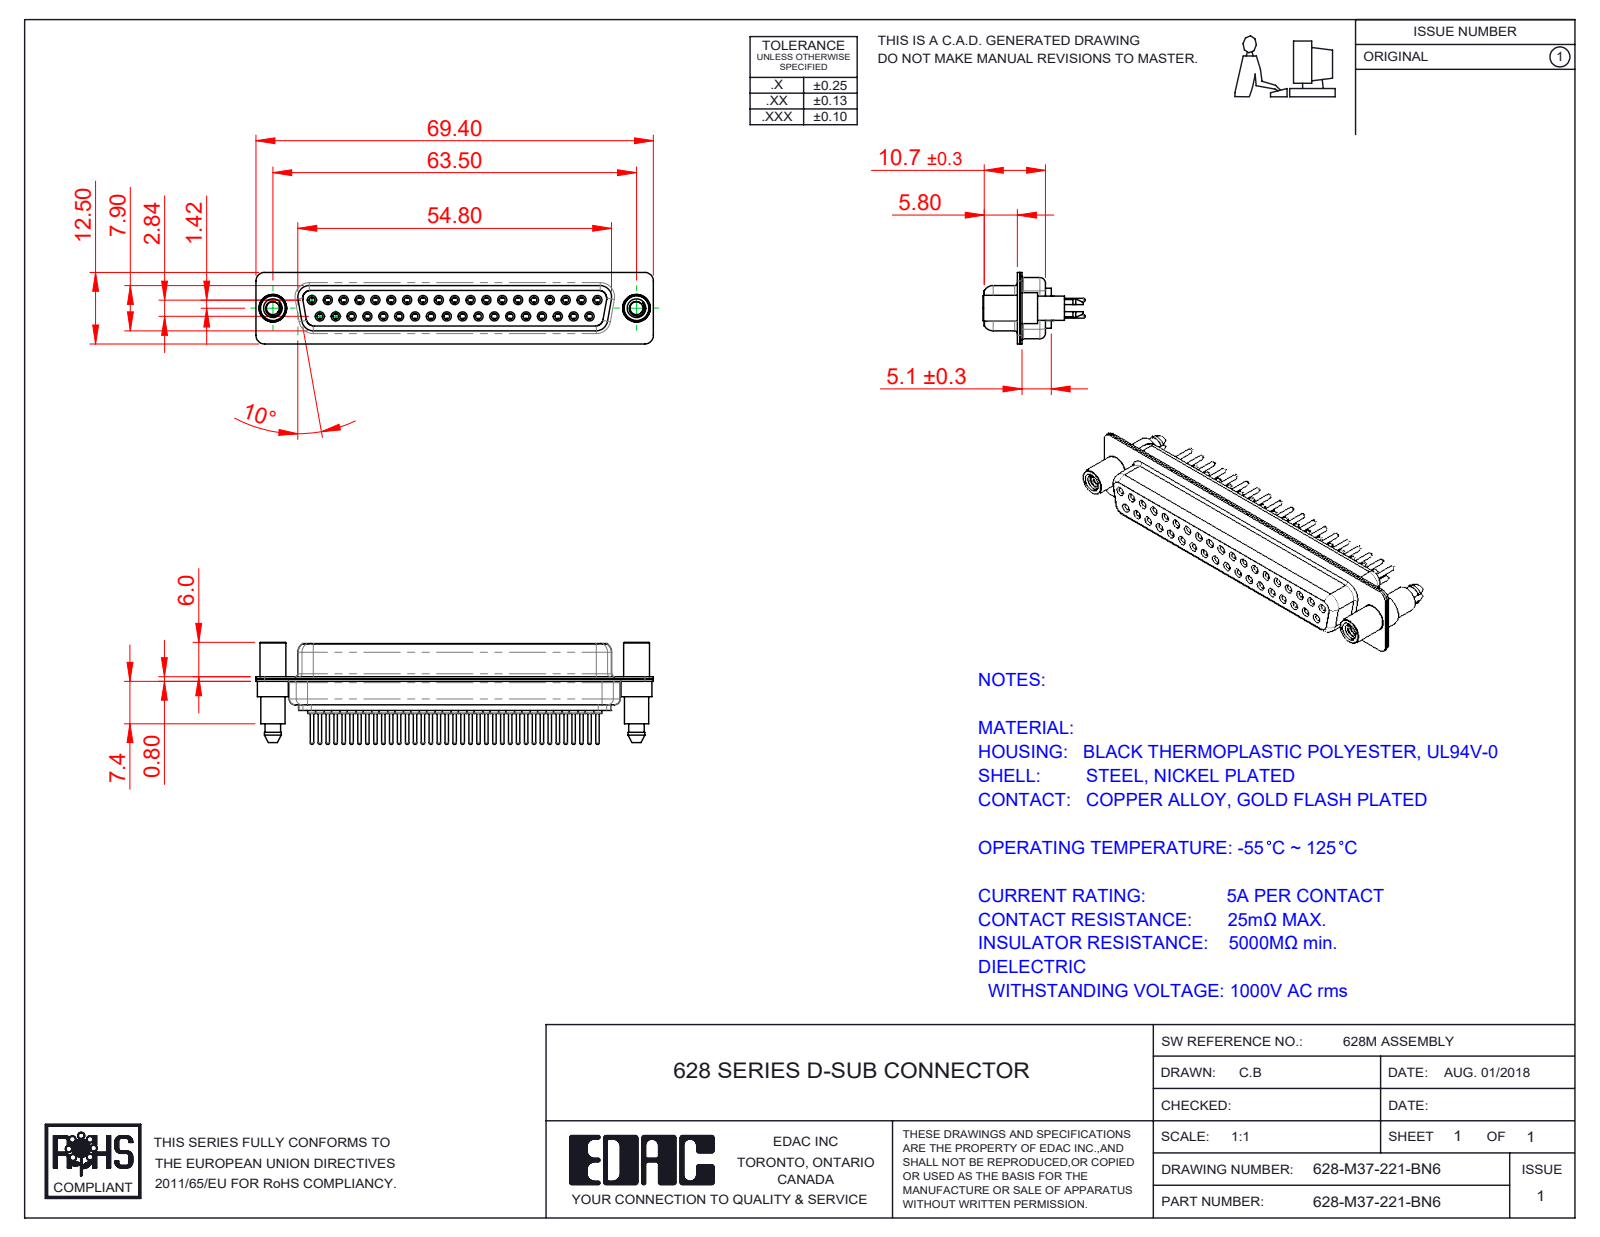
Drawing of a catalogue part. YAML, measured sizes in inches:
part_name: "628M Shell Front_37 Contacts; 628M Contact Row 2_21; 628M Shell Rear_37 Contacts; 628M Housing_37 Contacts (+3 more)"
step_written_by: "SolidWorks 2020 (CONFIG_CONTROL_DESIGN)"
units: inches
bodies: {solids: 42, faces: 2366, planar: 640, cylindrical: 868, other: 858}
overall_size: [2.732, 0.701, 0.492]
volume: 0.341
surface_area: 20.36
round_holes:
  - {diameter: 0.039, count: 37}
  - {diameter: 0.043, count: 37}
  - {diameter: 0.067, count: 37}
  - {diameter: 0.071, count: 37}
  - {diameter: 0.079, count: 37}
  - {diameter: 0.089, count: 2}
  - {diameter: 0.157, count: 2}
  - {diameter: 0.189, count: 2}
round_bosses_or_shafts:
  - {diameter: 0.087, count: 37}
  - {diameter: 0.063, count: 37}
  - {diameter: 0.059, count: 37}
  - {diameter: 0.024, count: 37}
  - {diameter: 0.213, count: 2}
  - {diameter: 0.193, count: 2}
  - {diameter: 0.177, count: 2}
  - {diameter: 0.167, count: 2}
partial_cylinders:
  - {radius: 0.059, count: 18}
  - {radius: 0.079, count: 12}
  - {radius: 0.063, count: 10}
  - {radius: 0.053, count: 8}
  - {radius: 0.01, count: 4}
  - {radius: 0.02, count: 4}
  - {radius: 0.024, count: 4}
  - {radius: 0.026, count: 4}
face_to_face_distances: [0.016, 0.055, 0.018, 0.333, 0.35, 0.071, 0.244, 0.278, 0.039, 0.073]
hole_center_spacings: [0.109, 0.218, 0.327, 0.124, 0.436, 0.545, 0.654, 0.763]
